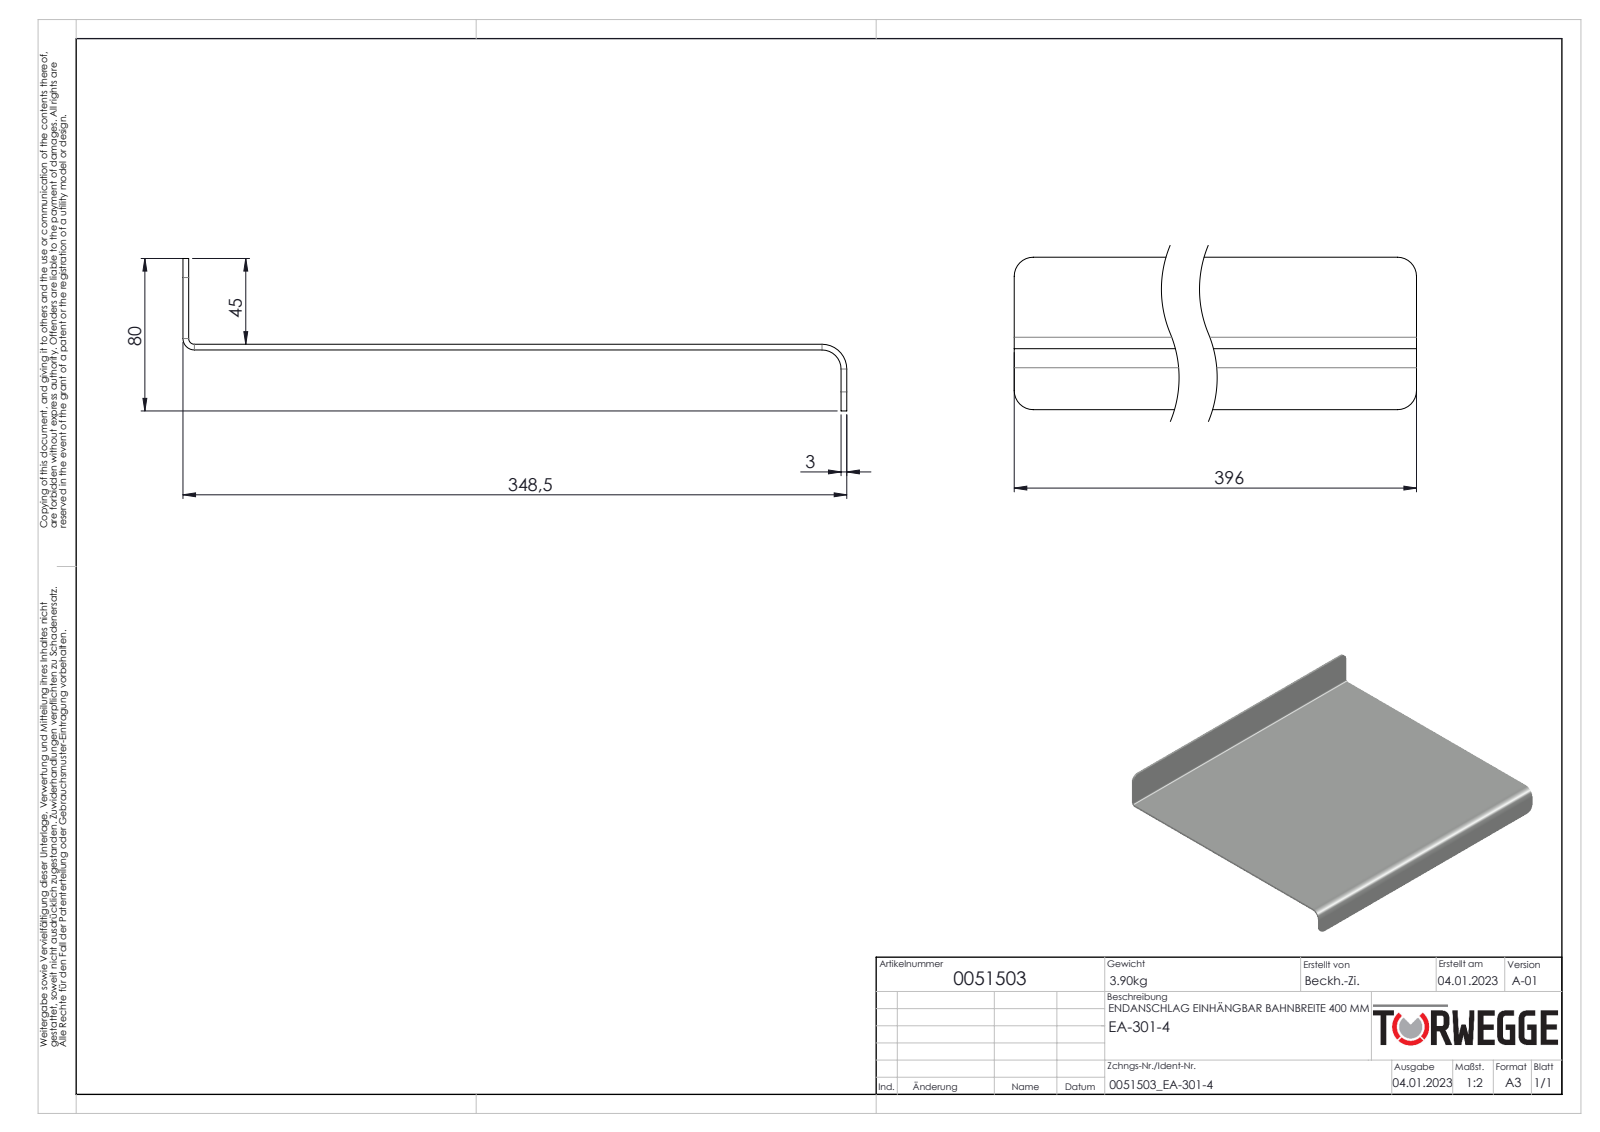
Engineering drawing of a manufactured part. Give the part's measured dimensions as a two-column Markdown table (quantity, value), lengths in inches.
| quantity | value |
| --- | --- |
| part name | 0051503 |
| STEP written by | SolidWorks 2020 (AUTOMOTIVE_DESIGN) |
| units | inches |
| bodies | 1 solid, 26 faces (18 planar, 8 cylindrical, 0 other) |
| overall size | 15.591 × 13.72 × 3.15 |
| volume | 30.33 in³ |
| surface area | 521.1 in² |
| partial cylindrical surfaces (radius × count) | 0.394 × 5, 0.118 × 1, 0.236 × 1, 0.512 × 1 |
| main face-to-face distances | 0.118, 13.602, 13.484, 13.72, 15.591, 1.26, 1.378, 3.15, 1.89, 1.772 |
